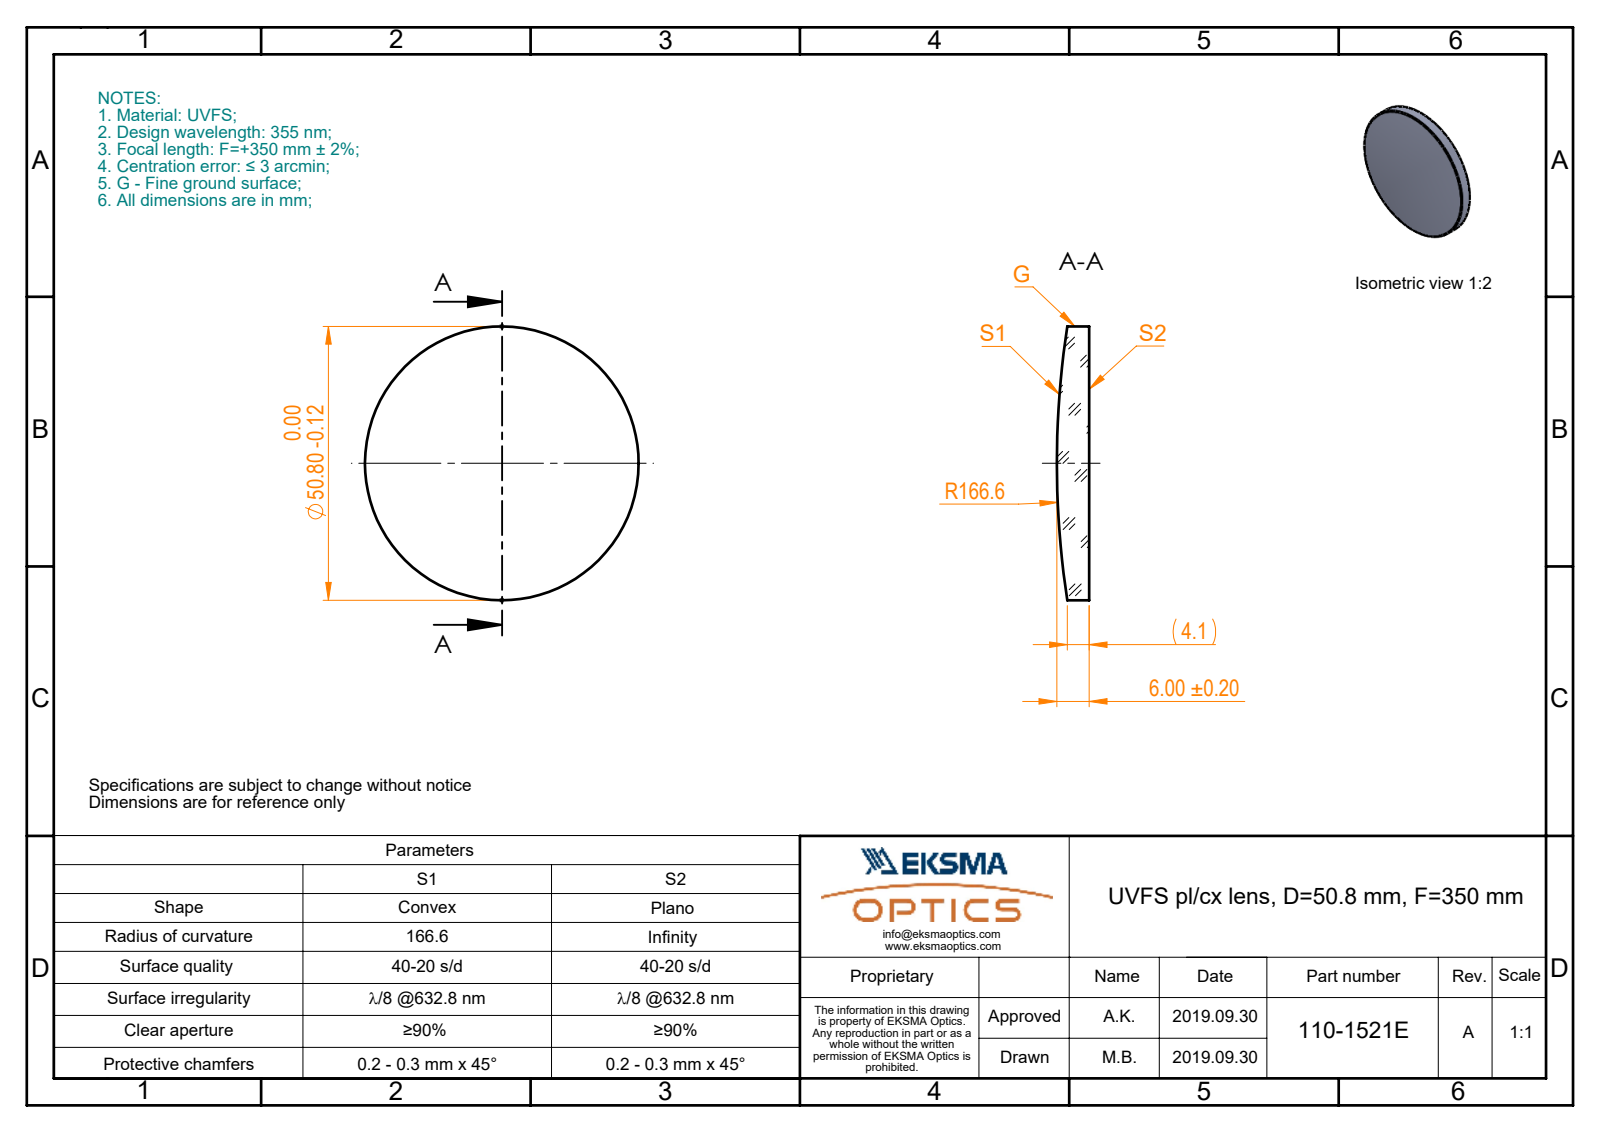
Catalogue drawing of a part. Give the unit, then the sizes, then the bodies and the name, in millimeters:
Units: millimetres
Overall size (bounding box): 50.8 × 50.8 × 6
Round bosses / shafts (diameter × count): ⌀50.8 ×1
Volume: 10 191 mm³ · Surface area: 4 712 mm²
Bodies: 1 solid, 4 faces (1 planar, 2 cylindrical, 1 other)
Part name (STEP PRODUCT): 110-1521E UVFS pl-cx 50.8 F350
STEP written by: SolidWorks 2019 (CONFIG_CONTROL_DESIGN)
